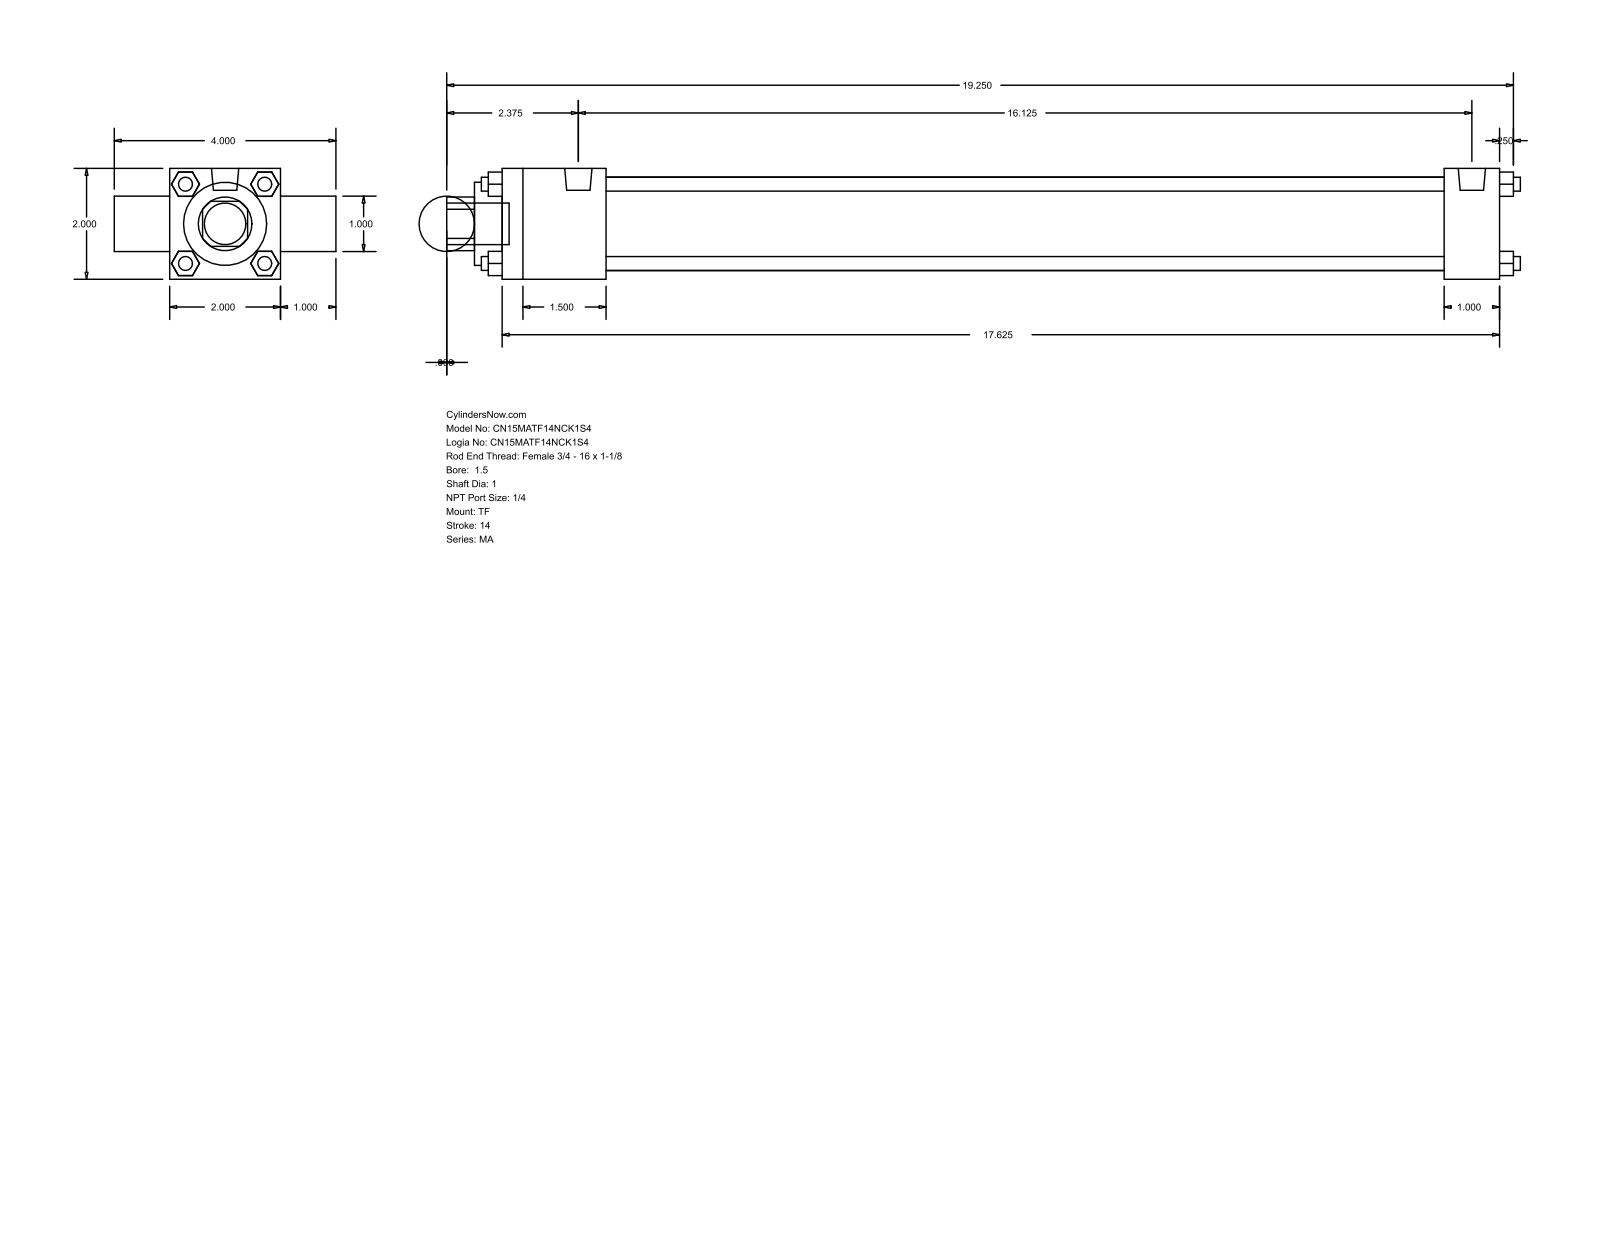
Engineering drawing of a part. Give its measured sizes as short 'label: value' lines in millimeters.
name: MA_TF__0150_1
written by: GSSL Pune (CONFIG_CONTROL_DESIGN)
unit: mm
bodies: 0 solids, 120 faces (92 planar, 28 cylindrical, 0 other)
size: 492.12 × 101.6 × 50.8
holes: 2× ⌀25.4, 1× ⌀38.1, 1× ⌀42.93
bosses: 4× ⌀6.35, 3× ⌀7.94, 2× ⌀12.49, 1× ⌀19.05
rounds: 1× R12.29
face distances: 50.8, 25.4, 457.2, 76.2, 6.35, 47.63, 431.8, 384.17, 409.57, 469.9
